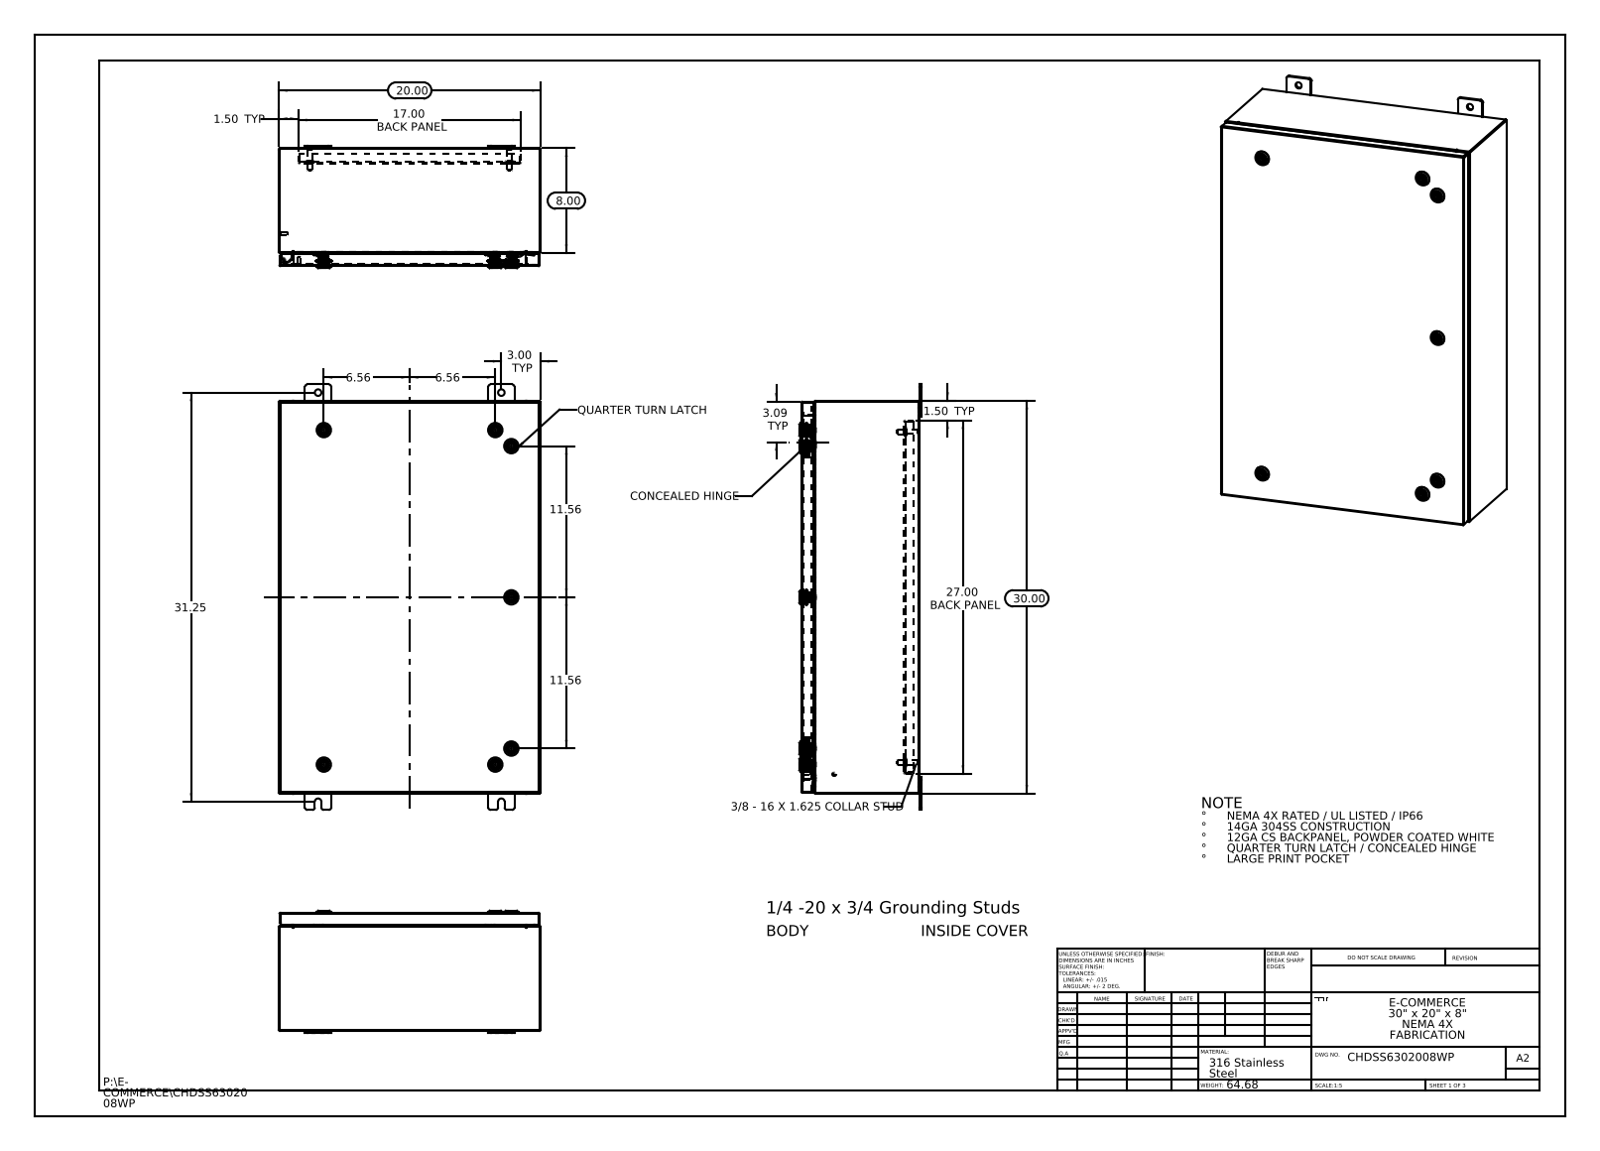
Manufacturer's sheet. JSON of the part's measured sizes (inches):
{"part_name": "CHDSS6302008WP Body; CHDSS6302008WP Top; CHDSS6302008WP Mounting Feet; CHDSS6302008WP Backpanel (+8 more)", "step_written_by": "SolidWorks 2013 (CONFIG_CONTROL_DESIGN)", "units": "inches", "bodies": {"solids": 61, "faces": 6252, "planar": 1822, "cylindrical": 1948, "other": 2482}, "overall_size": [32.5, 20, 9.356], "volume_in3": 230.9, "surface_area_in2": 5742, "round_holes": [[0.5, 8], [0.197, 7], [0.394, 7], [0.4, 7], [0.63, 7], [0.787, 7], [0.136, 4], [0.211, 1]], "round_bosses_or_shafts": [[0.236, 9], [1.102, 7], [0.78, 7], [0.626, 7], [0.61, 7], [0.531, 7], [0.392, 7], [0.114, 7]], "partial_cylinders_radius": [[0.006, 231], [0.118, 231], [0.028, 84], [0.02, 28], [0.197, 28], [0.19, 24], [0.013, 22], [0.088, 18]], "face_to_face_distances": [0.075, 0.074, 9.01, 8.935, 8.936, 8.861, 0.104, 19.925, 1, 1.075], "hole_center_spacings": [0.688, 1.858, 3.065, 11.55, 13.1, 14, 14.164, 14.187]}
